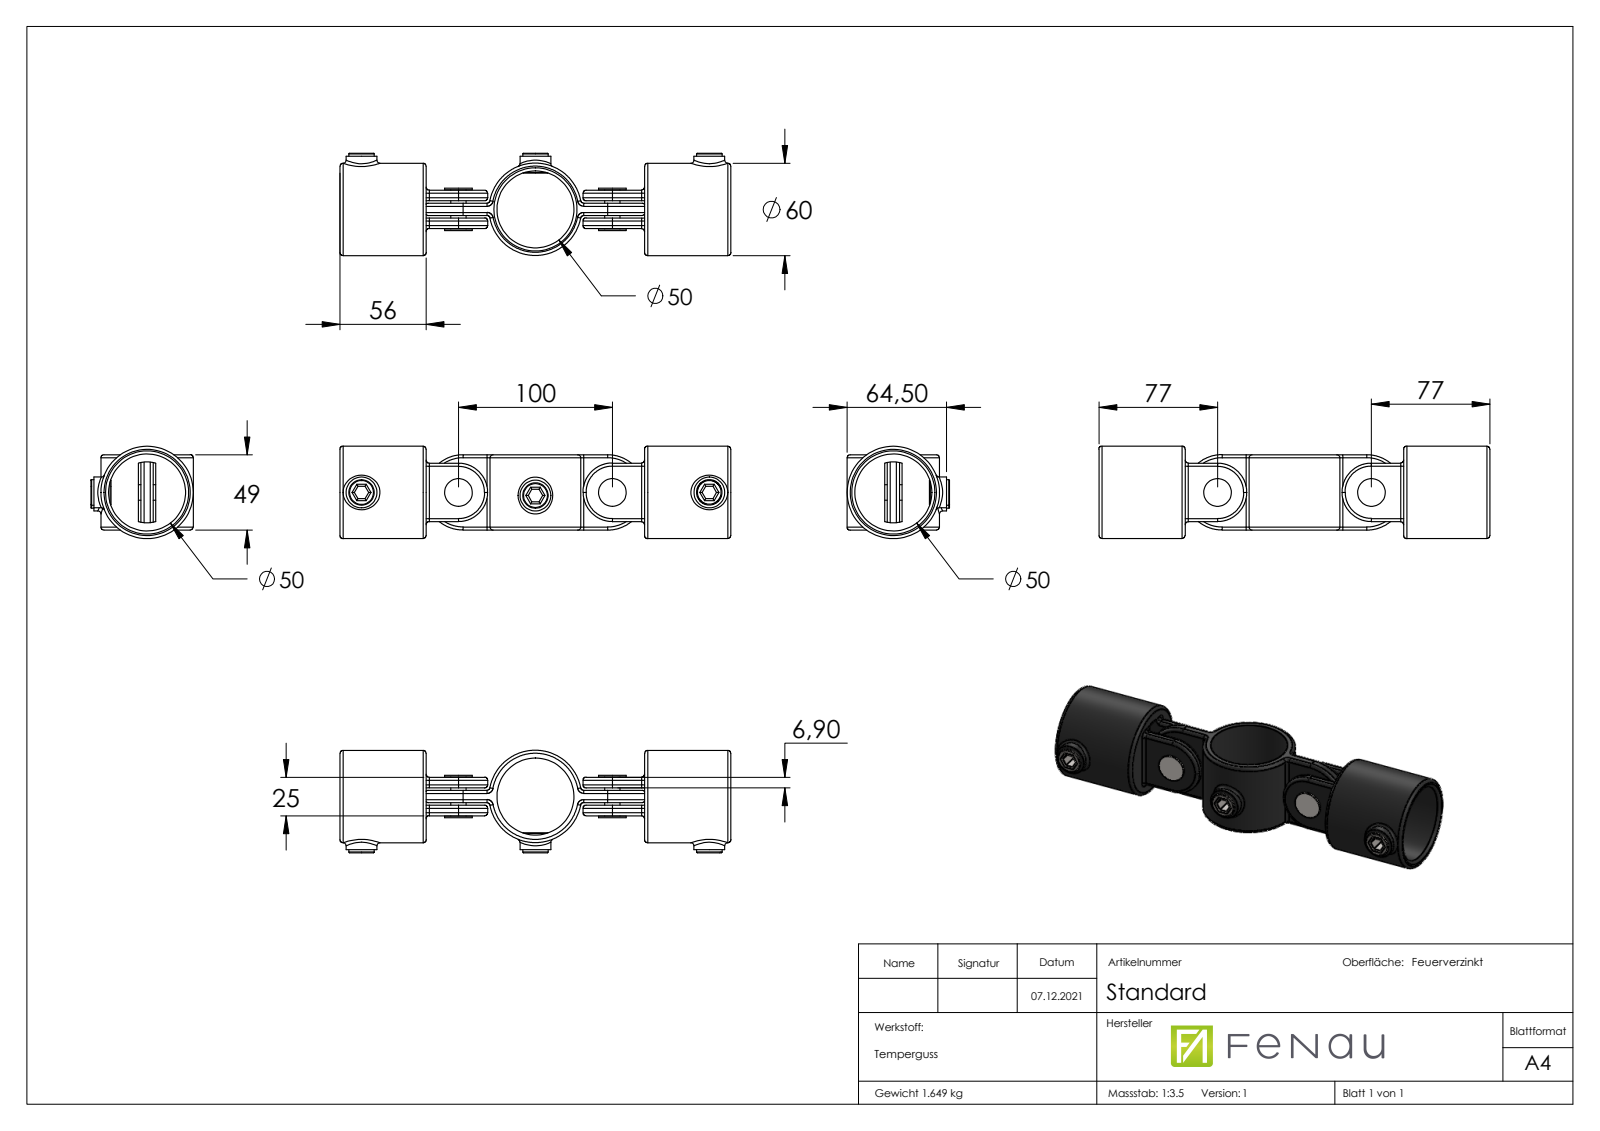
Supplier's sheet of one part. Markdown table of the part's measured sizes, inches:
| quantity | value |
| --- | --- |
| part name | 167-D48 Teil4; 167-D48 Teil2; 167-D48; 167-D48 Teil3 (+1 more) |
| STEP written by | SolidWorks 2018 (CONFIG_CONTROL_DESIGN) |
| units | inches |
| bodies | 8 solids, 253 faces (63 planar, 118 cylindrical, 72 other) |
| overall size | 10 × 2.618 × 2.362 |
| volume | 13.73 in³ |
| surface area | 144.9 in² |
| round holes (diameter × count) | 0.6 × 3, 0.413 × 2, 1.969 × 2 |
| round bosses / shafts (diameter × count) | 0.787 × 3, 0.65 × 3, 2.362 × 2, 0.709 × 2, 0.394 × 2 |
| partial cylindrical surfaces (radius × count) | 0.079 × 56, 0.748 × 2, 0.965 × 2, 0.78 × 1 |
| main face-to-face distances | 0.063, 0.378, 0.272, 0.335, 0.65, 0.713, 0.315, 0.441, 0.197, 5.787 |
| hole center spacings | 1.97, 2.48, 4.45, 6.417, 3.937, 8.898 |
